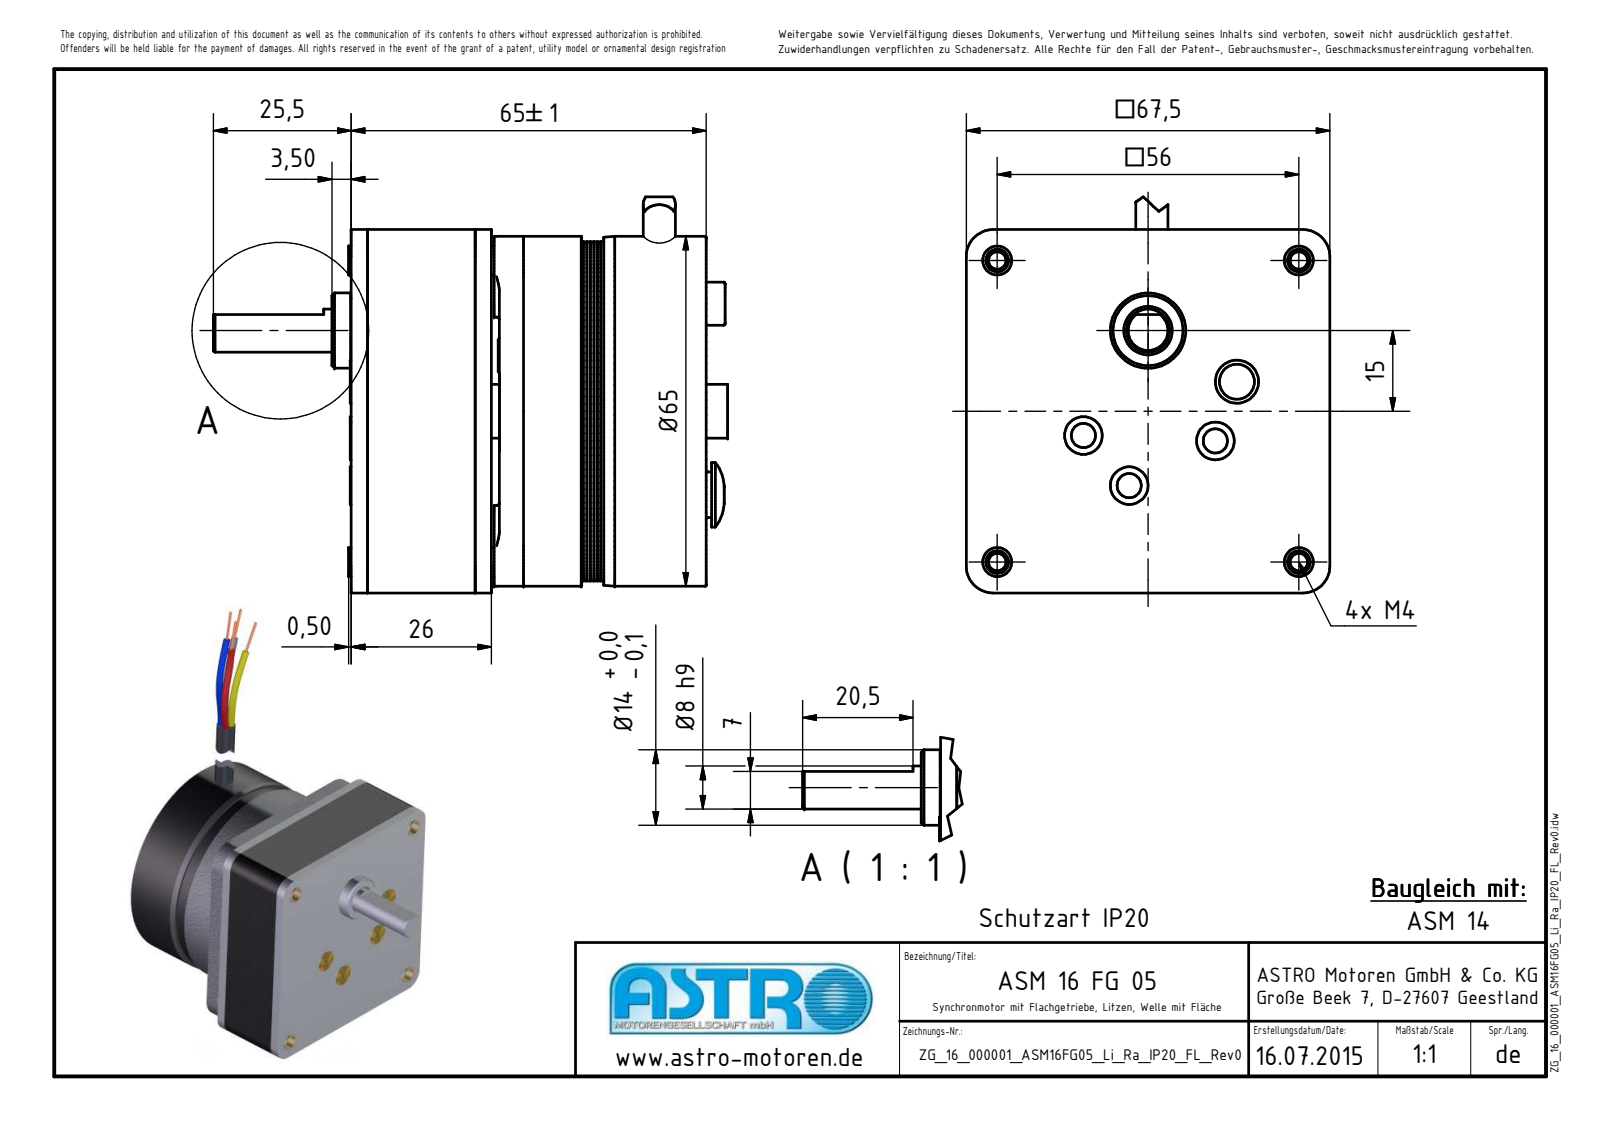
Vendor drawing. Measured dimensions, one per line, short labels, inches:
name: ZG_16_000001_ASM16FG05_Li_Ra_IP20_FL_Rev0; AFG-05_Welle_FL_20,5; FG-Antriebsseite; FG-Abstandhalter (+8 more)
written by: Autodesk Inventor 2010 (AUTOMOTIVE_DESIGN)
unit: in
bodies: 53 solids, 4690 faces (1734 planar, 2800 cylindrical, 156 other)
size: 5.077 × 3.76 × 2.657
volume: 6.871 in³; area: 240.5 in²
holes: 8× ⌀0.063, 8× ⌀0.161, 4× ⌀0.173, 4× ⌀0.197, 3× ⌀0.177, 1× ⌀0.217, 1× ⌀0.236, 1× ⌀0.256, 1× ⌀0.315, 1× ⌀0.472, 1× ⌀0.551, 1× ⌀0.61
bosses: 6× ⌀0.315, 4× ⌀0.591, 4× ⌀0.212, 4× ⌀0.191, 4× ⌀0.157, 4× ⌀0.141, 3× ⌀0.276, 3× ⌀0.031
rounds: 48× R0.02, 8× R0.089, 8× R0.138, 4× R0.118, 4× R0.197, 4× R0.207, 1× R0.236, 1× R0.433
face distances: 0.026, 0.051, 0.077, 0.102, 0.128, 0.154, 0.179, 0.205, 0.118, 0.23
hole spacings: 1.239, 0.444, 1.964, 0.889, 1.104, 1.161, 1.643, 1.85
